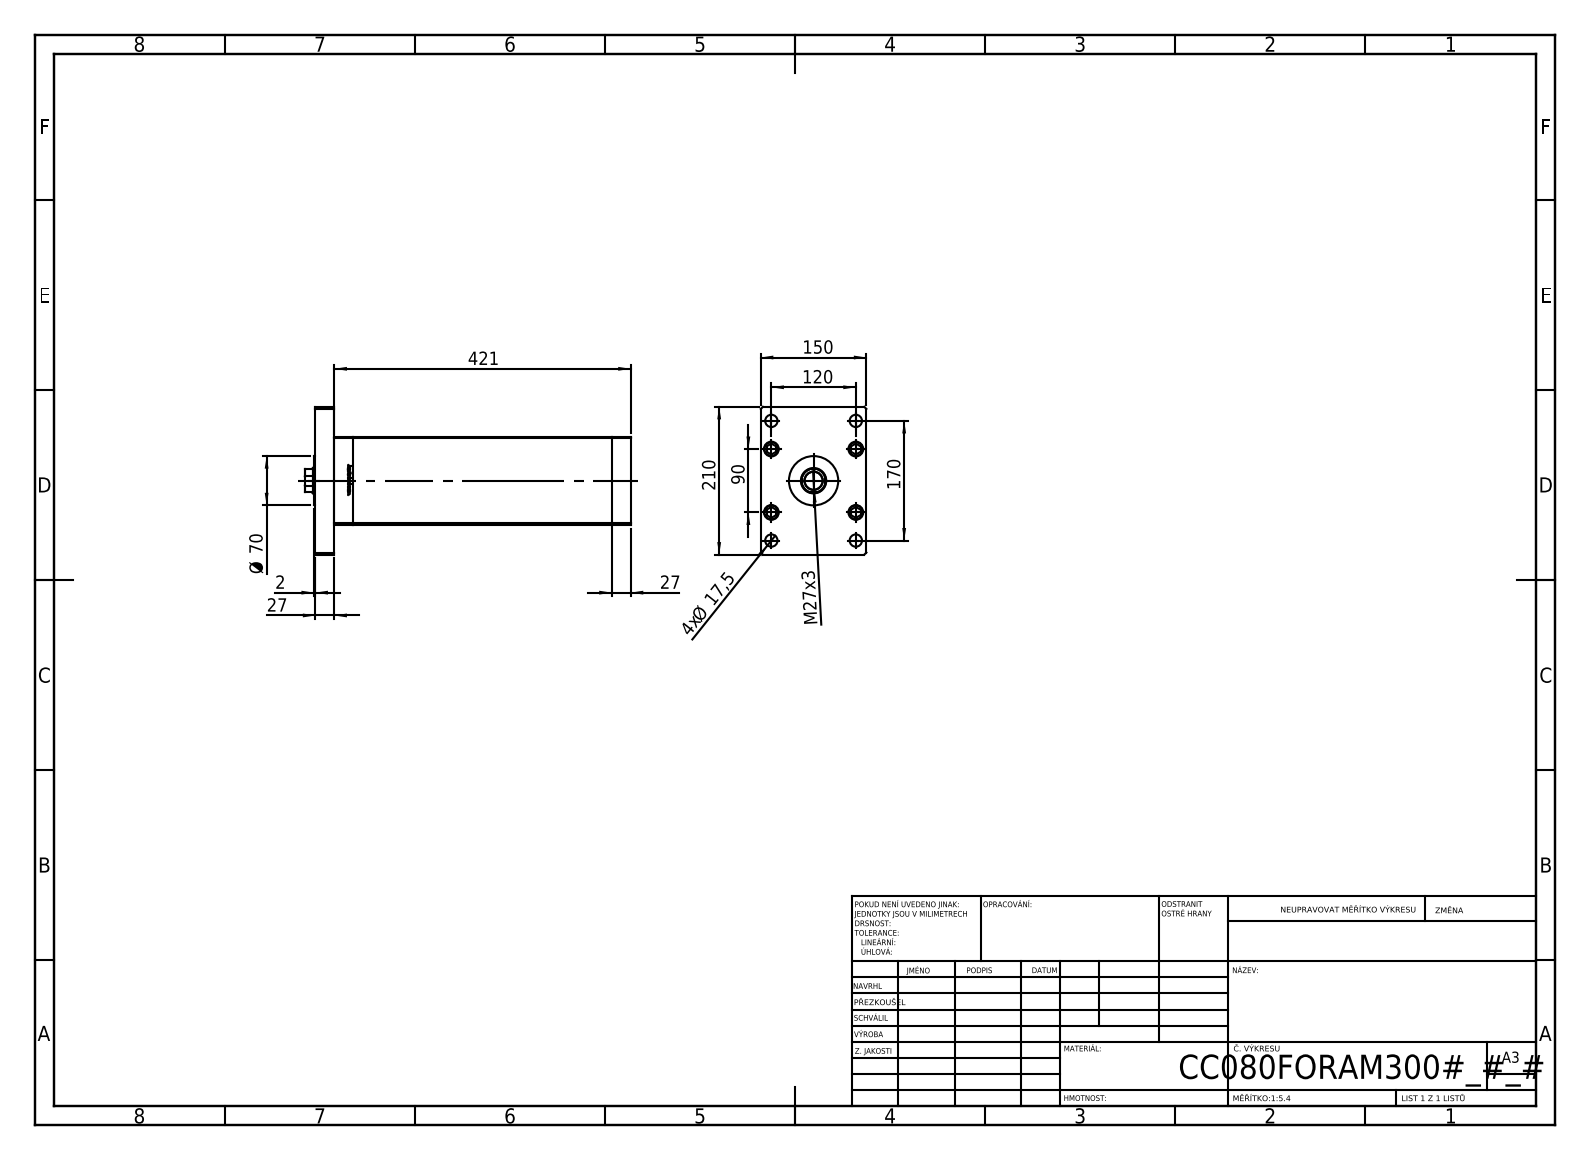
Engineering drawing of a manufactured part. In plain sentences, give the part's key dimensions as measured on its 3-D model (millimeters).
The part is named "ALLEN BOLT; V220C_F_MIDDLE; V220C BACK_F; V220C_FRONT_F (+2 more)". Its 3-D file was written by "SolidWorks 2019 (CONFIG_CONTROL_DESIGN)". It is 19 solids with 1298 faces: 513 planar, 179 cylindrical and 606 other. Overall it measures 463 by 210 by 150 millimeters. Its volume is 7 275 000 cubic millimeters and its surface area 657 603 square millimeters. Round holes: 9 of diameter 17.5, 5 of diameter 22, 4 of diameter 16, 4 of diameter 21, 1 of diameter 25.5, 1 of diameter 36, 1 of diameter 37.5. Round bosses or shafts: 9 of diameter 8, 5 of diameter 21, 1 of diameter 80, 1 of diameter 70. Partial cylindrical surfaces (rounded edges, fillets, slot ends): 2 of radius 0.93, 1 of radius 17.5. The main face-to-face distances are 27, 150, 125, 394, 421, 367, 54, 448, 33.5, 6.5. The hole center spacings are 51, 40, 75, 104.04, 120, 126.49, 130, 176.92.
